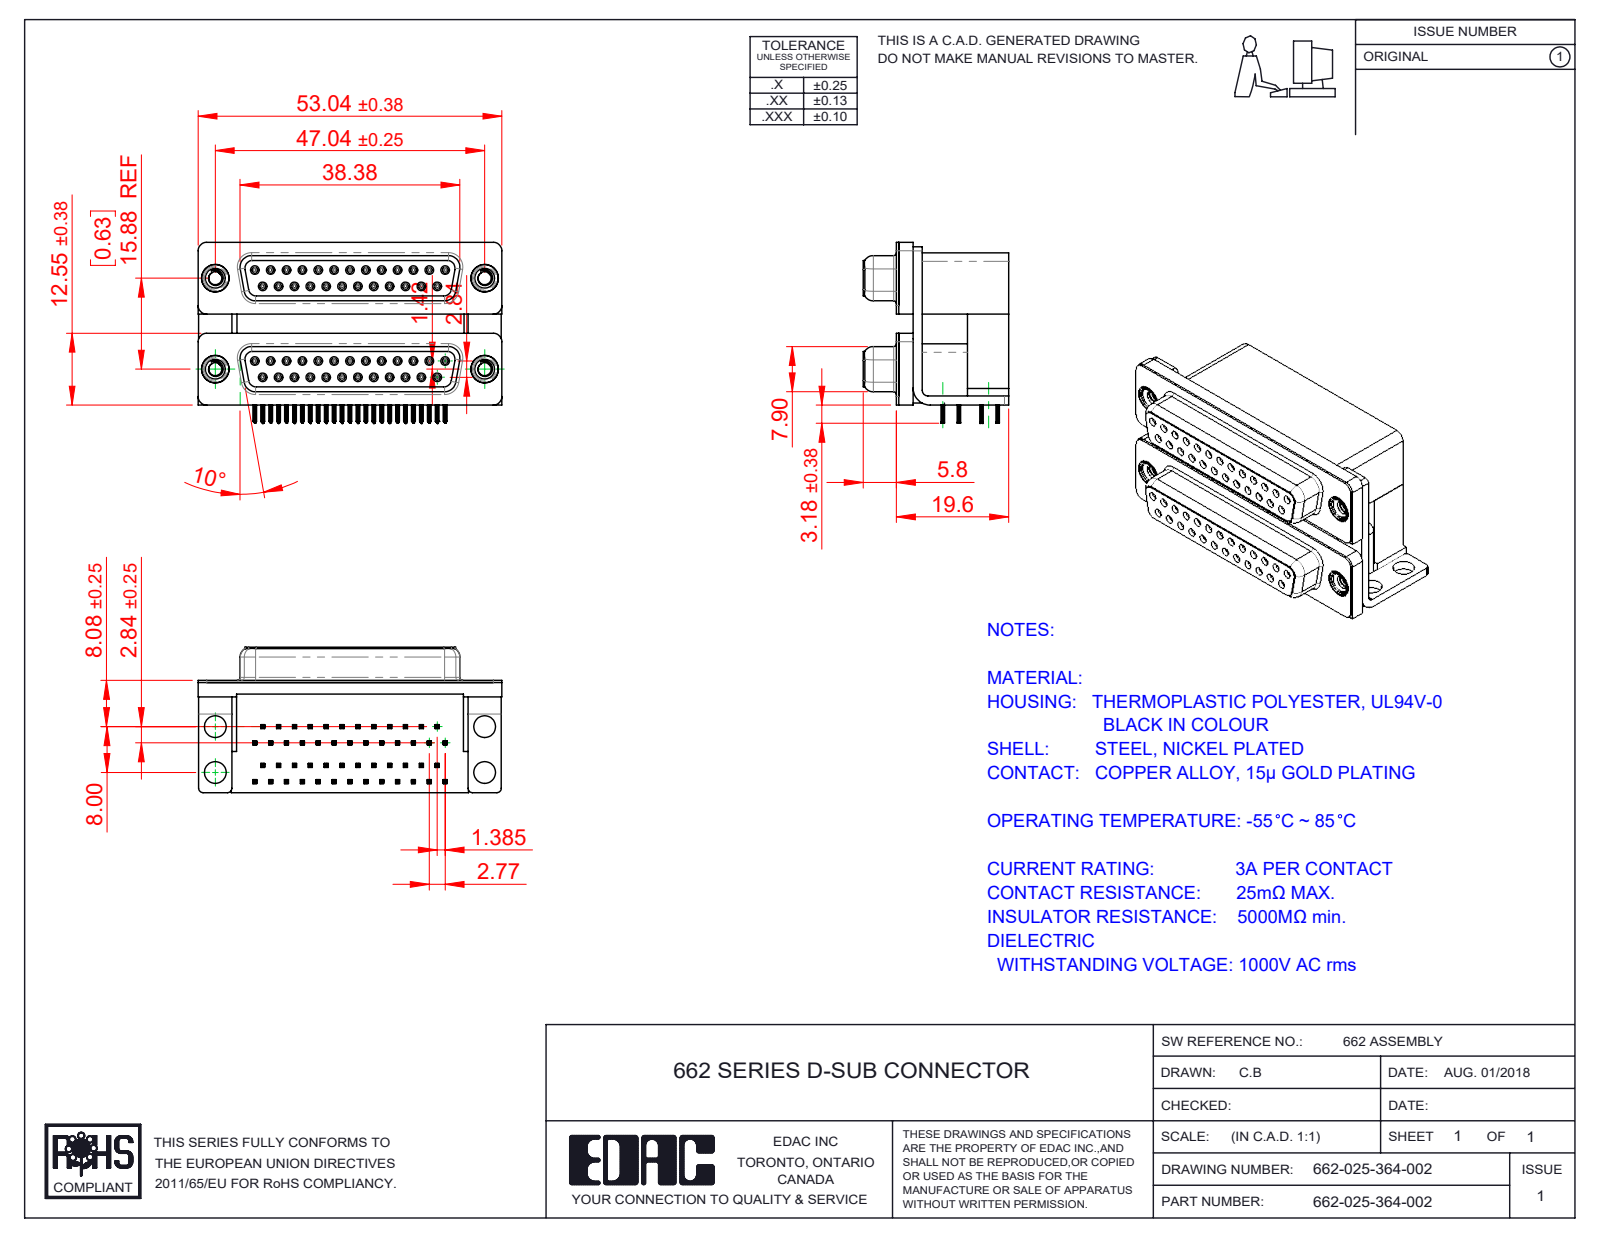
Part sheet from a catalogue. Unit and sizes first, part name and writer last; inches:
Units: inches
Overall size (bounding box): 2.088 × 1.244 × 1
Round holes (diameter × count): ⌀0.031 ×50, ⌀0.035 ×50, ⌀0.089 ×4, ⌀0.138 ×4, ⌀0.15 ×4, ⌀0.157 ×4, ⌀0.189 ×4, ⌀0.197 ×4
Round bosses / shafts (diameter × count): ⌀0.047 ×50, ⌀0.193 ×4, ⌀0.187 ×4, ⌀0.154 ×4
Partial cylindrical surfaces — rounded edges, fillets, slot ends (radius × count): R0.004 ×400, R0.006 ×200, R0.014 ×100, R0.013 ×50, R0.011 ×24, R0.053 ×18, R0.059 ×13, R0.02 ×8
Main face-to-face distances: 0.625, 0.756, 0.016, 0.283, 0.472, 0.421, 0.244, 0.657, 0.374, 0.098
Hole centre spacings: 0.124, 0.109, 0.218, 0.436, 0.327, 0.198, 0.545, 0.294
Volume: 1.396 in³ · Surface area: 38.66 in²
Bodies: 61 solids, 7792 faces (3576 planar, 1804 cylindrical, 2412 other)
Part name (STEP PRODUCT): 662 Housing Spacer_25 Contacts L; 662 Contact Bottom Lower; 662 Shell_25 Contacts; 662 Contact Top Lower (+7 more)
STEP written by: SolidWorks 2020 (CONFIG_CONTROL_DESIGN)
